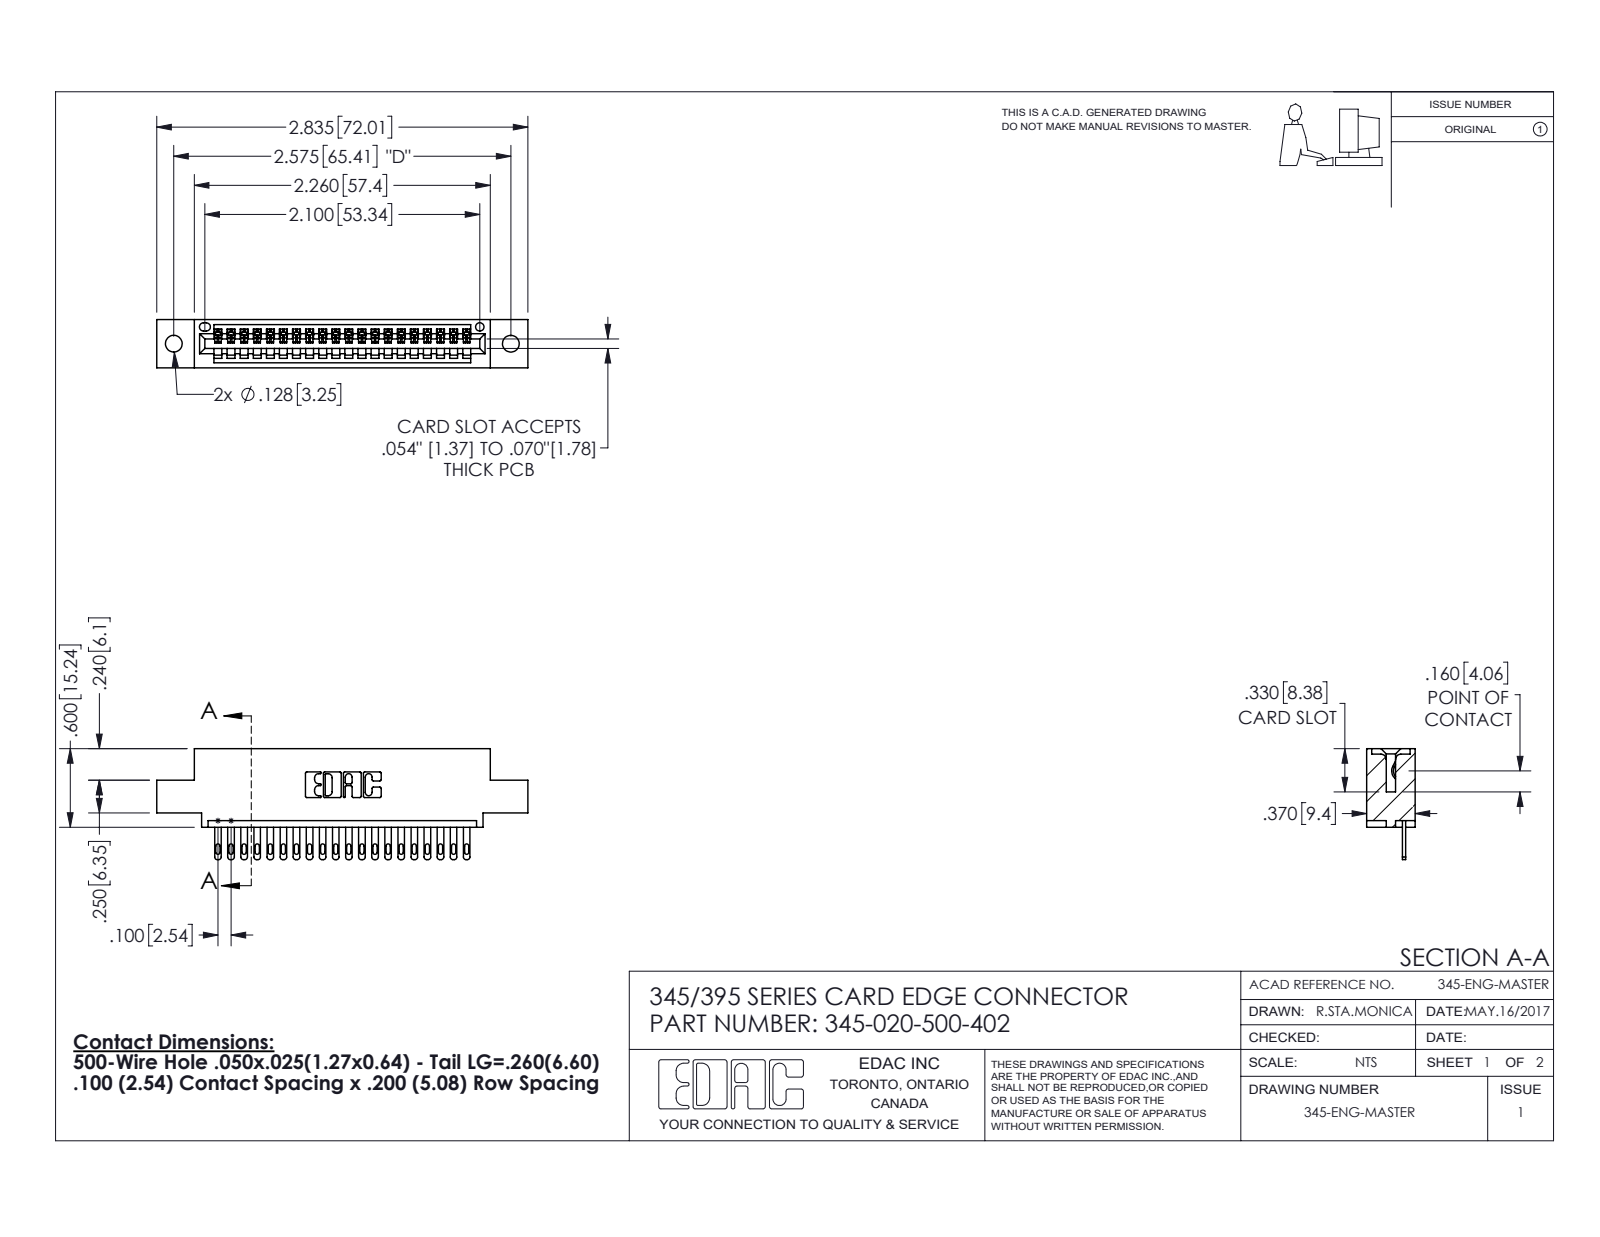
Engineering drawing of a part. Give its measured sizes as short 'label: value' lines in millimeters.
name: 345-020-500-402; 345-292-001_345-293-100; 345 Part_0.110 Offset - 0.128 Dia
written by: SolidWorks 2016 (CONFIG_CONTROL_DESIGN)
unit: mm
bodies: 21 solids, 1210 faces (764 planar, 446 cylindrical, 0 other)
size: 72 × 21.5 × 9.4
volume: 6 550 mm³; area: 8 277 mm²
holes: 2× ⌀3.3, 1× ⌀1.6
rounds: 40× R0.2, 40× R0.4, 40× R0.5, 22× R0.3, 6× R0.2, 6× R0.8, 3× R0.7, 2× R0.8
face distances: 7.6, 1.8, 9.4, 5.1, 2.5, 6.9, 0.6, 5.7, 3.8, 15.2
hole spacings: 6.9, 59.5, 65.4
